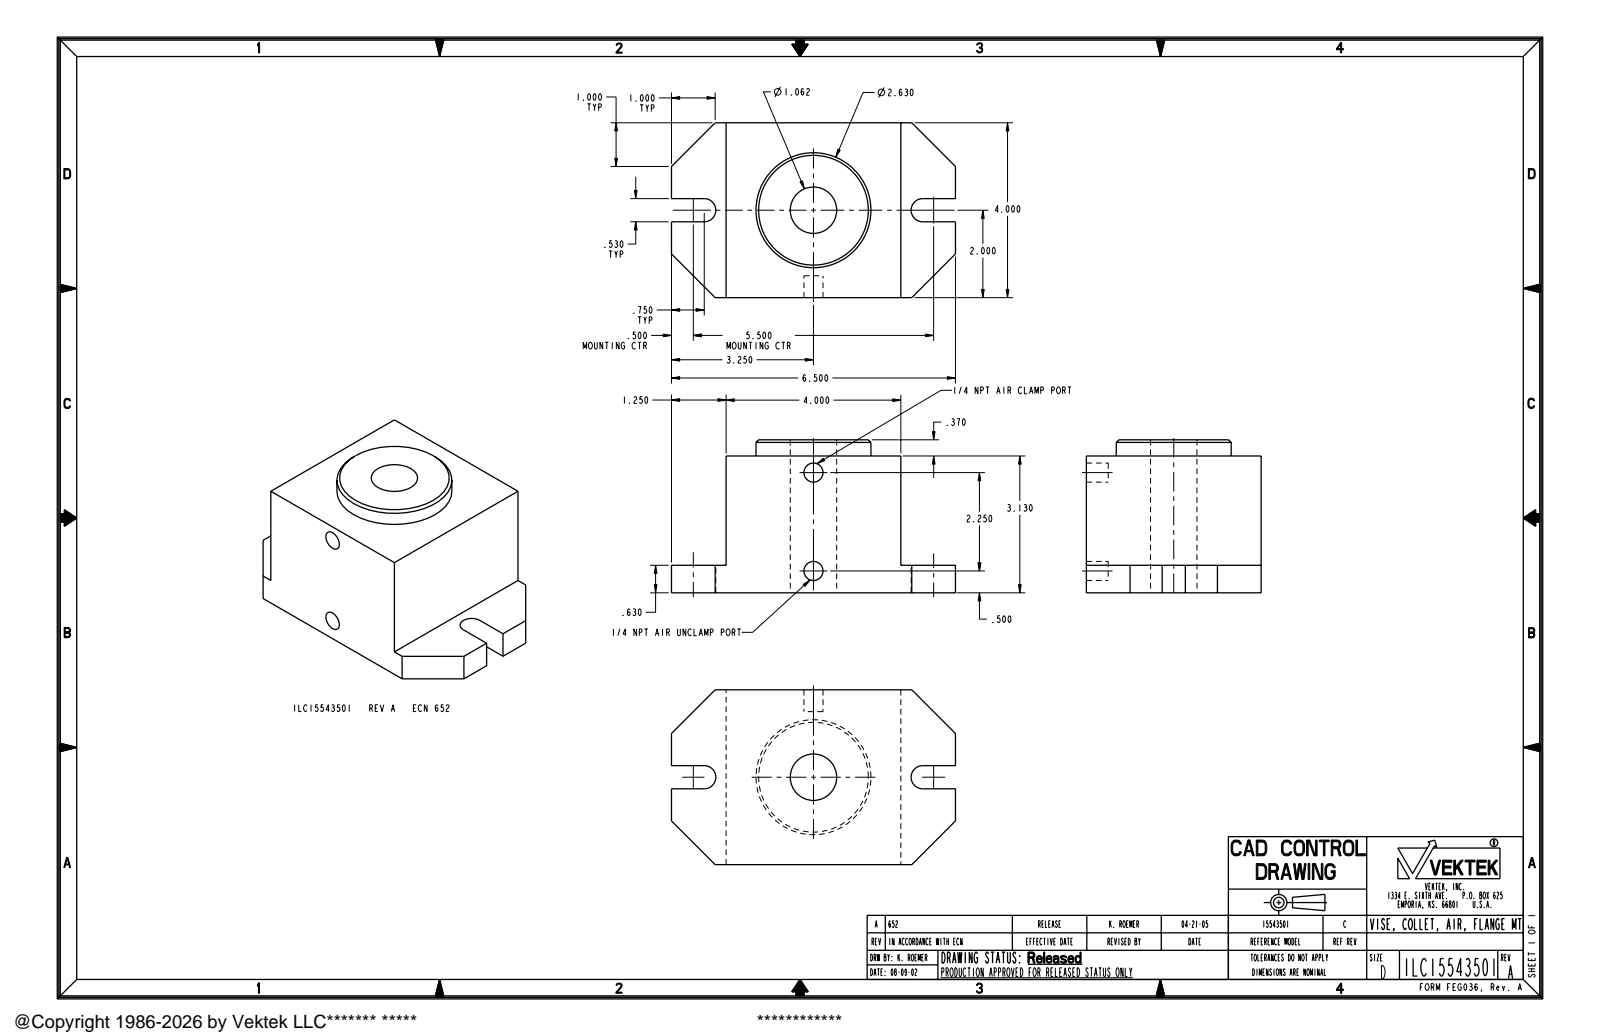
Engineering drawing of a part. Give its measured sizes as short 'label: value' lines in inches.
name: ILC15543501
written by: PRO/ENGINEER BY PARAMETRIC TECHNOLOGY CORPORATION, 2004290 (AUTOMOTIVE_DESIGN_CC2)
unit: in
bodies: 1 solid, 35 faces (23 planar, 10 cylindrical, 2 other)
size: 6.5 × 4 × 3.5
volume: 53.23 in³; area: 114 in²
holes: 2× ⌀0.437, 1× ⌀1.062
bosses: 1× ⌀2.63
rounds: 2× R0.265
face distances: 4, 3.13, 0.63, 2.5, 3.5, 2.87, 0.37, 1.735, 2.265, 1.25
hole spacings: 2.25
